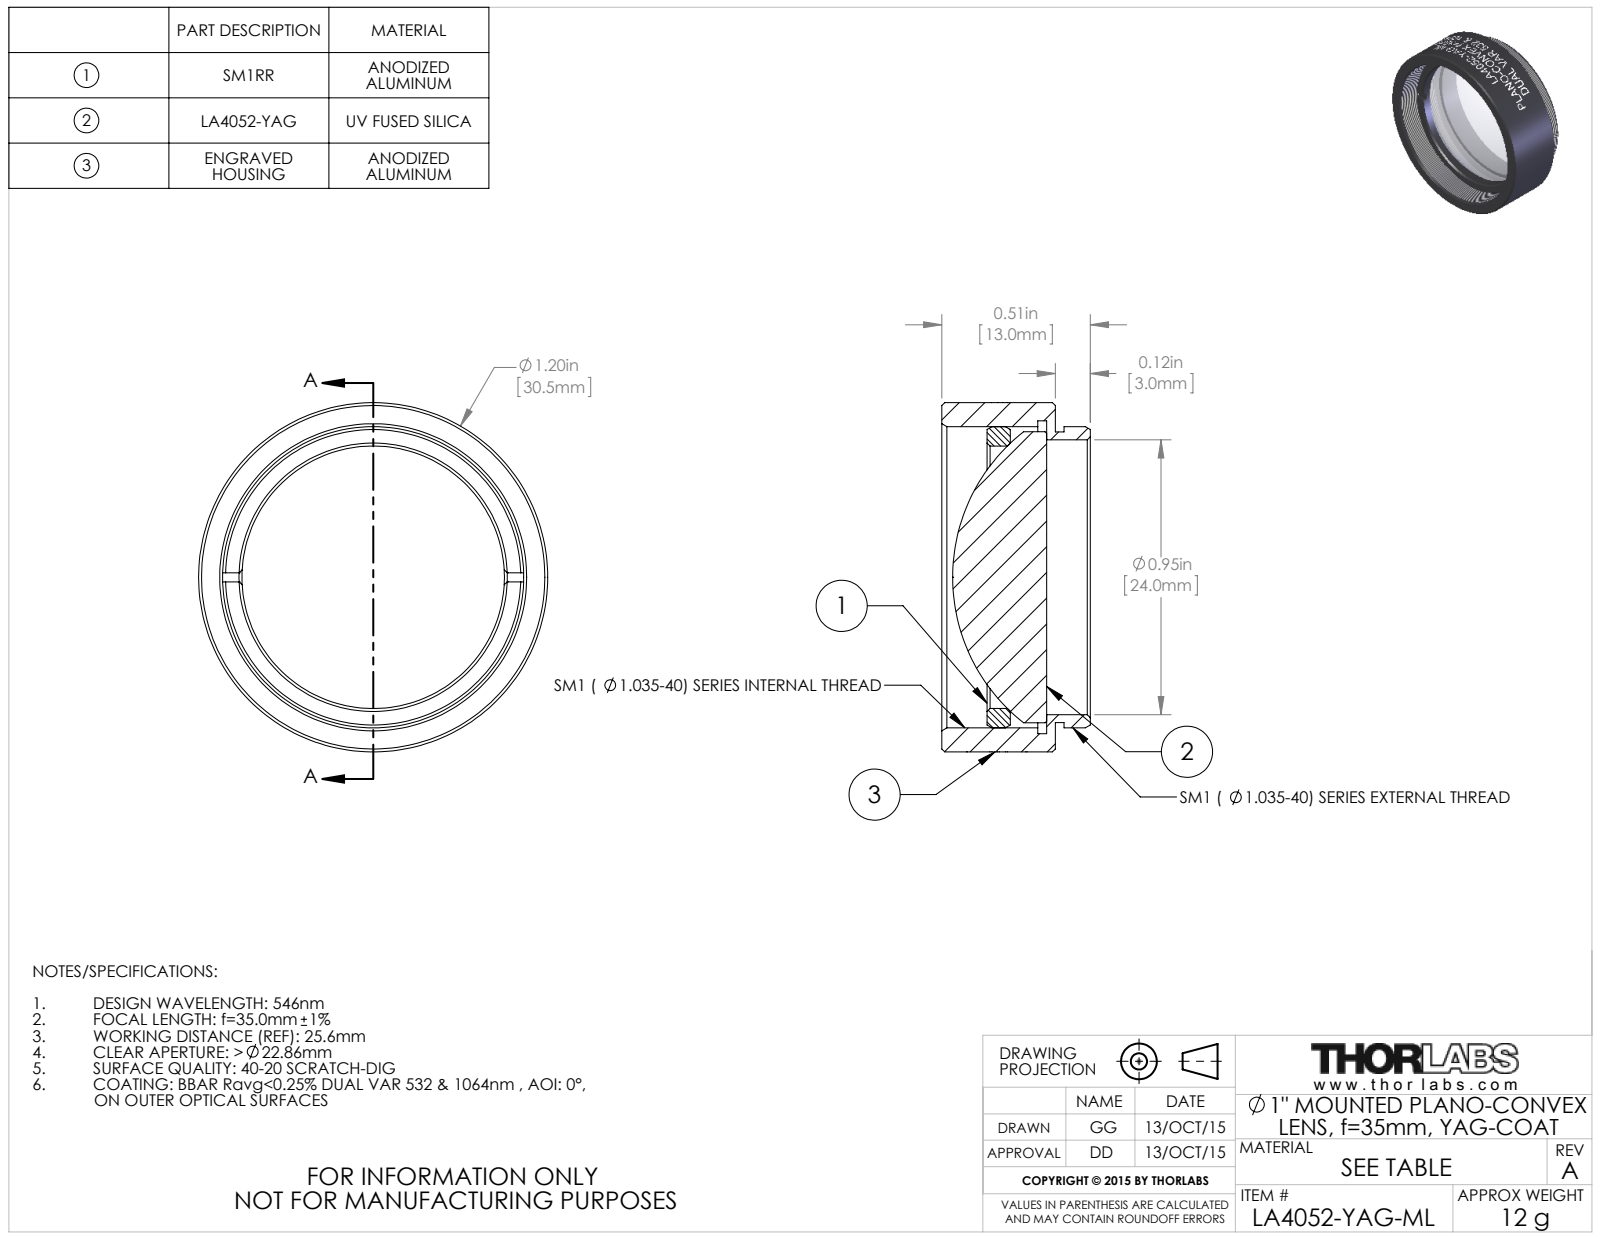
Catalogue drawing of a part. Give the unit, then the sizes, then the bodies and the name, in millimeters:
Units: millimetres
Overall size (bounding box): 30.48 × 30.48 × 12.95
Round holes (diameter × count): ⌀22.91 ×1, ⌀24 ×1, ⌀27.3 ×1
Round bosses / shafts (diameter × count): ⌀30.48 ×1, ⌀26.29 ×1, ⌀25.4 ×1, ⌀25.37 ×1
Main face-to-face distances: 0.76, 9.91, 9.15, 3.93, 3.17, 5.98, 5.96, 5.2, 2.03, 3.95
Volume: 5 075 mm³ · Surface area: 4 699 mm²
Bodies: 3 solids, 147 faces (20 planar, 101 cylindrical, 26 other)
Part name (STEP PRODUCT): TTN039132-E0W
STEP written by: SolidWorks 2014 (CONFIG_CONTROL_DESIGN)
